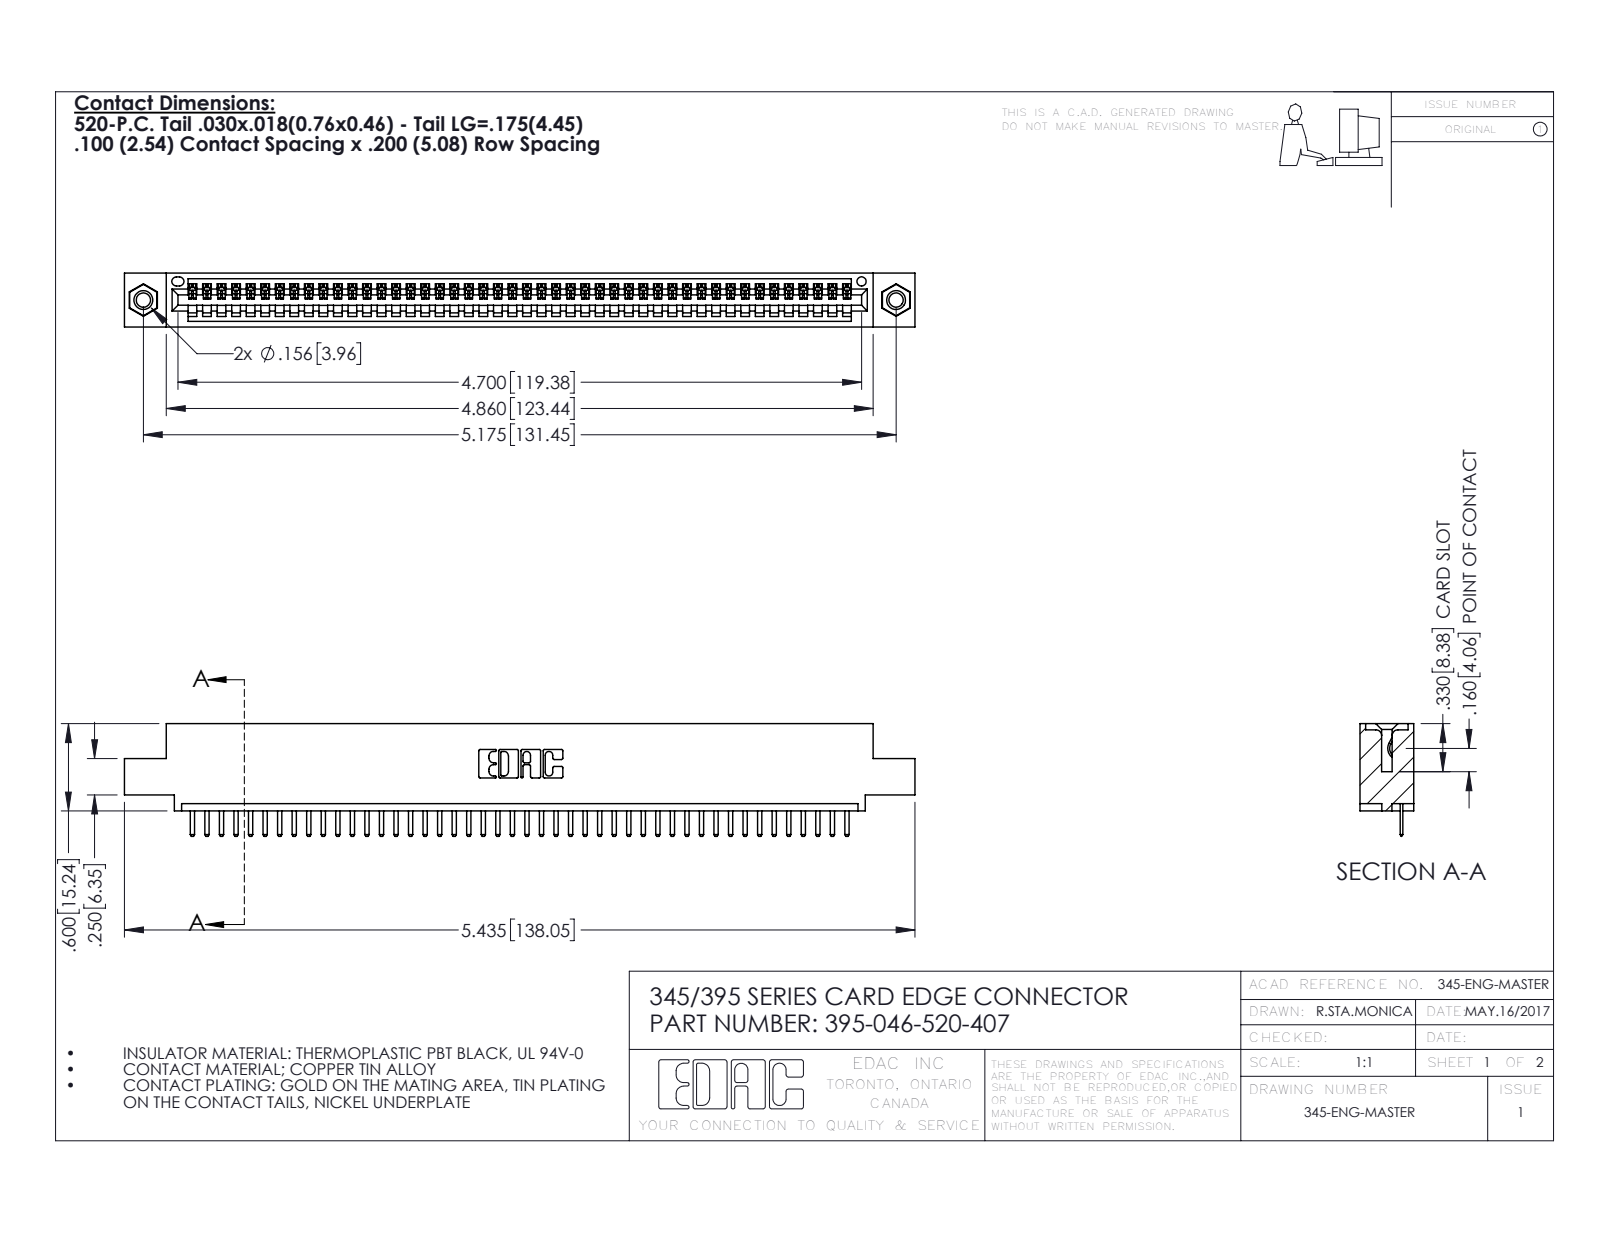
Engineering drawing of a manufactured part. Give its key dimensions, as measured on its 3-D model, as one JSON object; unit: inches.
{"part_name": "345-292-001_345-293-120; 345-250-001_345-250-005-103; 395-046-520-407; 345 Part_0.110 Offset - 0.156 Dia-TI", "step_written_by": "SolidWorks 2016 (CONFIG_CONTROL_DESIGN)", "units": "inches", "bodies": {"solids": 49, "faces": 3042, "planar": 2048, "cylindrical": 978, "other": 16}, "overall_size": [5.435, 0.775, 0.37], "volume_in3": 0.789, "surface_area_in2": 26.22, "round_holes": [[0.098, 2], [0.125, 2], [0.156, 2], [0.064, 1]], "round_bosses_or_shafts": [[0.155, 2]], "partial_cylinders_radius": [[0.01, 94], [0.006, 92], [0.01, 22], [0.007, 6], [0.031, 6], [0.026, 3], [0.031, 2], [0.04, 2]], "face_to_face_distances": [0.072, 0.298, 0.37, 0.2, 0.098, 0.272, 0.025, 0.225, 0.072, 0.149], "hole_center_spacings": [0.27, 4.939, 5.175]}
